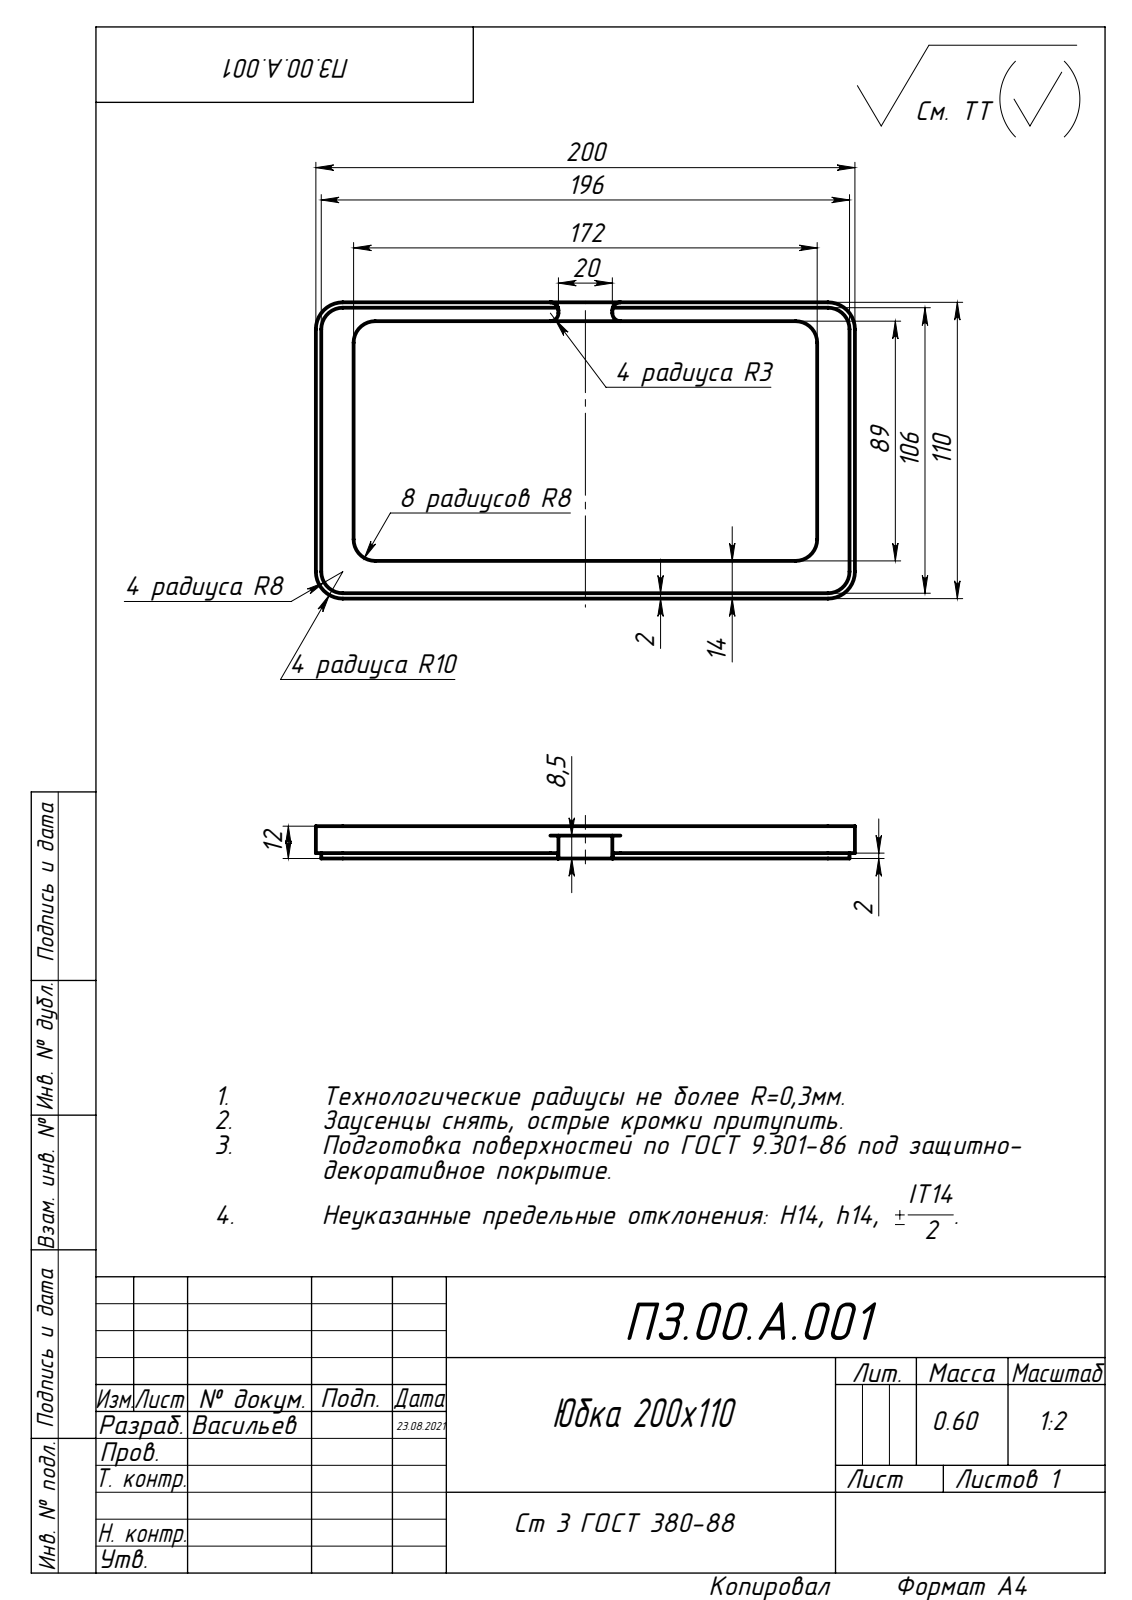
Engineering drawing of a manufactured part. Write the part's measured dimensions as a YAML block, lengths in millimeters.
part_name: "Юбка 200х110"
step_written_by: "SolidWorks 2018 (CONFIG_CONTROL_DESIGN)"
units: millimeters
bodies: {solids: 1, faces: 35, planar: 19, cylindrical: 16, other: 0}
overall_size: [200, 110, 12]
volume: 76379
surface_area: 26362
partial_cylinders:
  - {radius: 8, count: 8}
  - {radius: 3, count: 4}
  - {radius: 10, count: 4}
face_to_face_distances: [12, 14, 2, 186, 103, 89, 110, 96, 7, 10]
